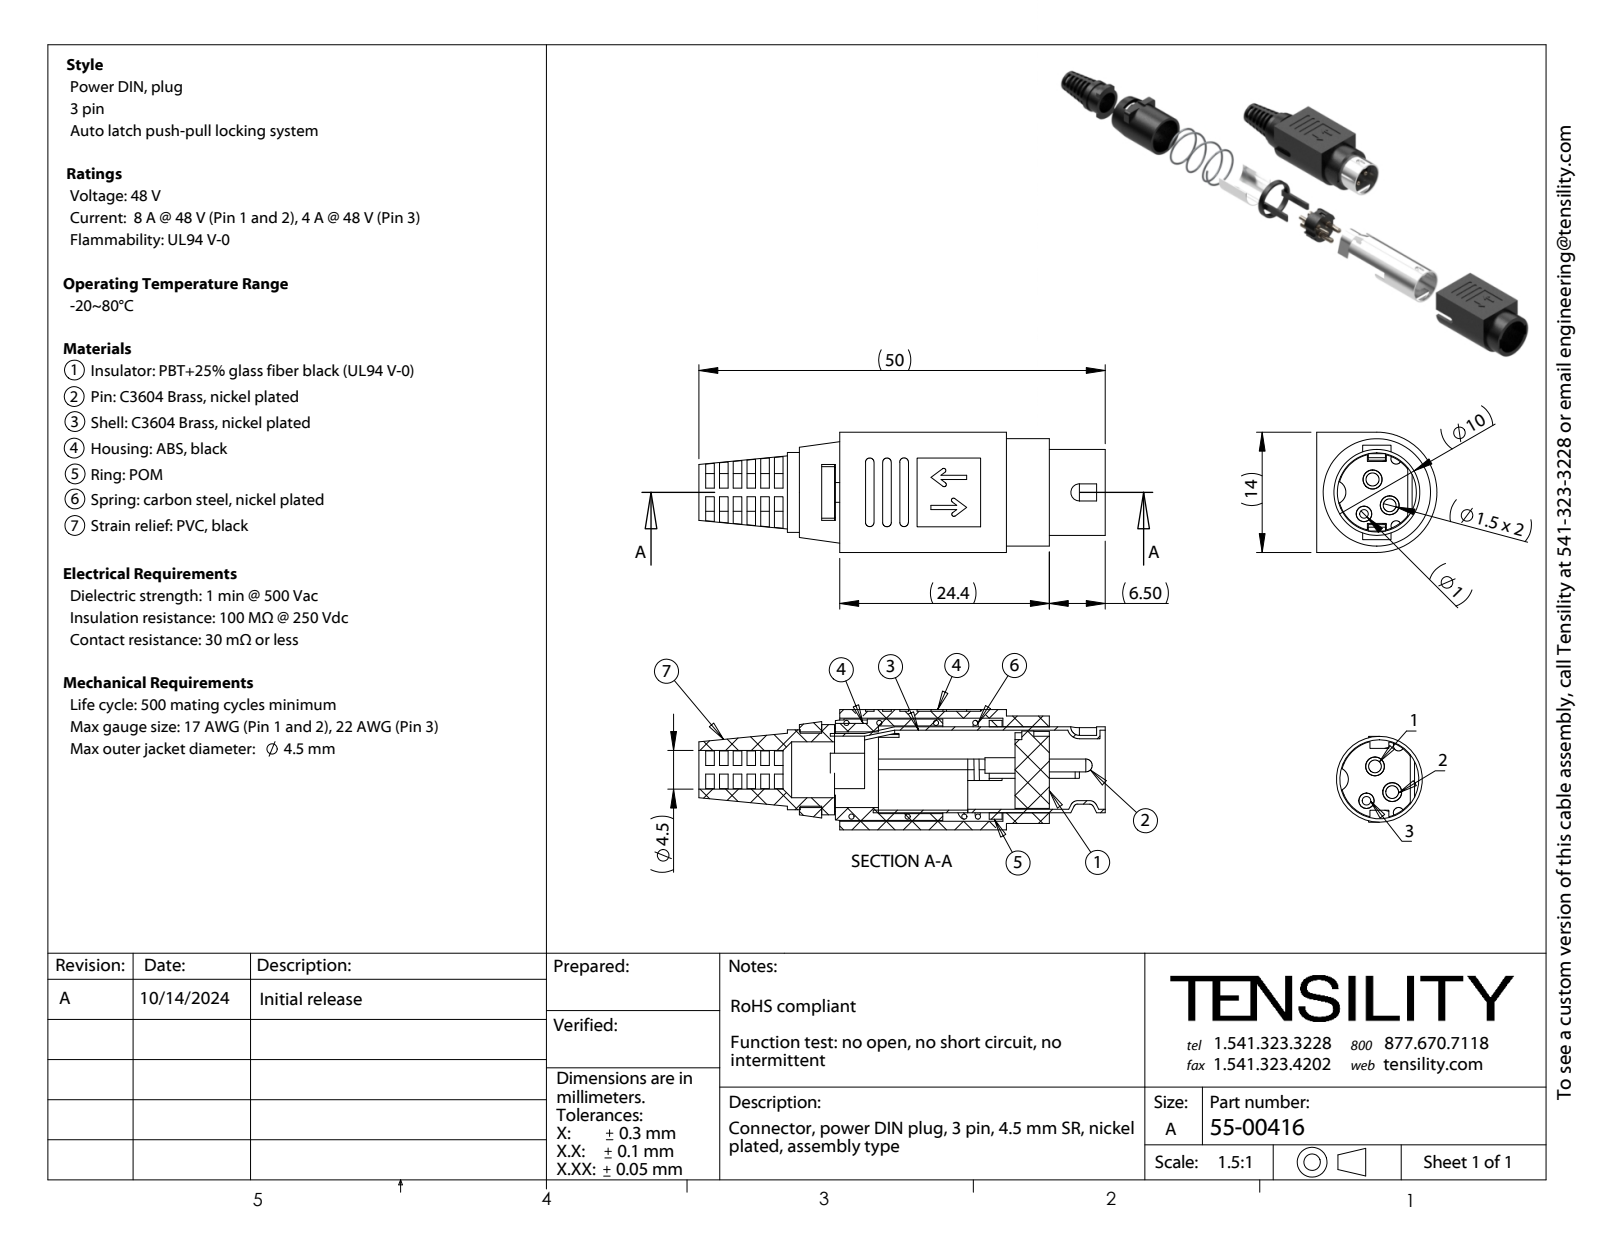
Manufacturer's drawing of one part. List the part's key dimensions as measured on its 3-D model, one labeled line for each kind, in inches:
Part name (STEP PRODUCT): 55-00416-05_默认; 55-00416-03_默认; 55-00416; 55-00416-08_默认 (+7 more)
STEP written by: SolidWorks 2025 (CONFIG_CONTROL_DESIGN)
Units: inches
Bodies: 11 solids, 403 faces (266 planar, 111 cylindrical, 26 other)
Overall size (bounding box): 1.862 × 0.551 × 0.551
Volume: 0.163 in³ · Surface area: 11.44 in²
Round holes (diameter × count): ⌀0.047 ×2, ⌀0.028 ×1, ⌀0.177 ×1, ⌀0.256 ×1, ⌀0.346 ×1, ⌀0.362 ×1, ⌀0.394 ×1, ⌀0.402 ×1
Round bosses / shafts (diameter × count): ⌀0.071 ×3, ⌀0.087 ×2, ⌀0.059 ×2, ⌀0.492 ×1, ⌀0.465 ×1, ⌀0.453 ×1, ⌀0.366 ×1, ⌀0.354 ×1
Partial cylindrical surfaces — rounded edges, fillets, slot ends (radius × count): R0.02 ×8, R0.039 ×4, R0.024 ×3, R0.01 ×2, R0.01 ×2, R0.035 ×2, R0.055 ×1, R0.059 ×1
Main face-to-face distances: 0.039, 0.512, 0.059, 0.063, 0.02, 0.472, 0.197, 0.217, 0.276, 0.024
Hole centre spacings: 0.062, 0.083, 0.115, 0.124, 0.142, 0.162
